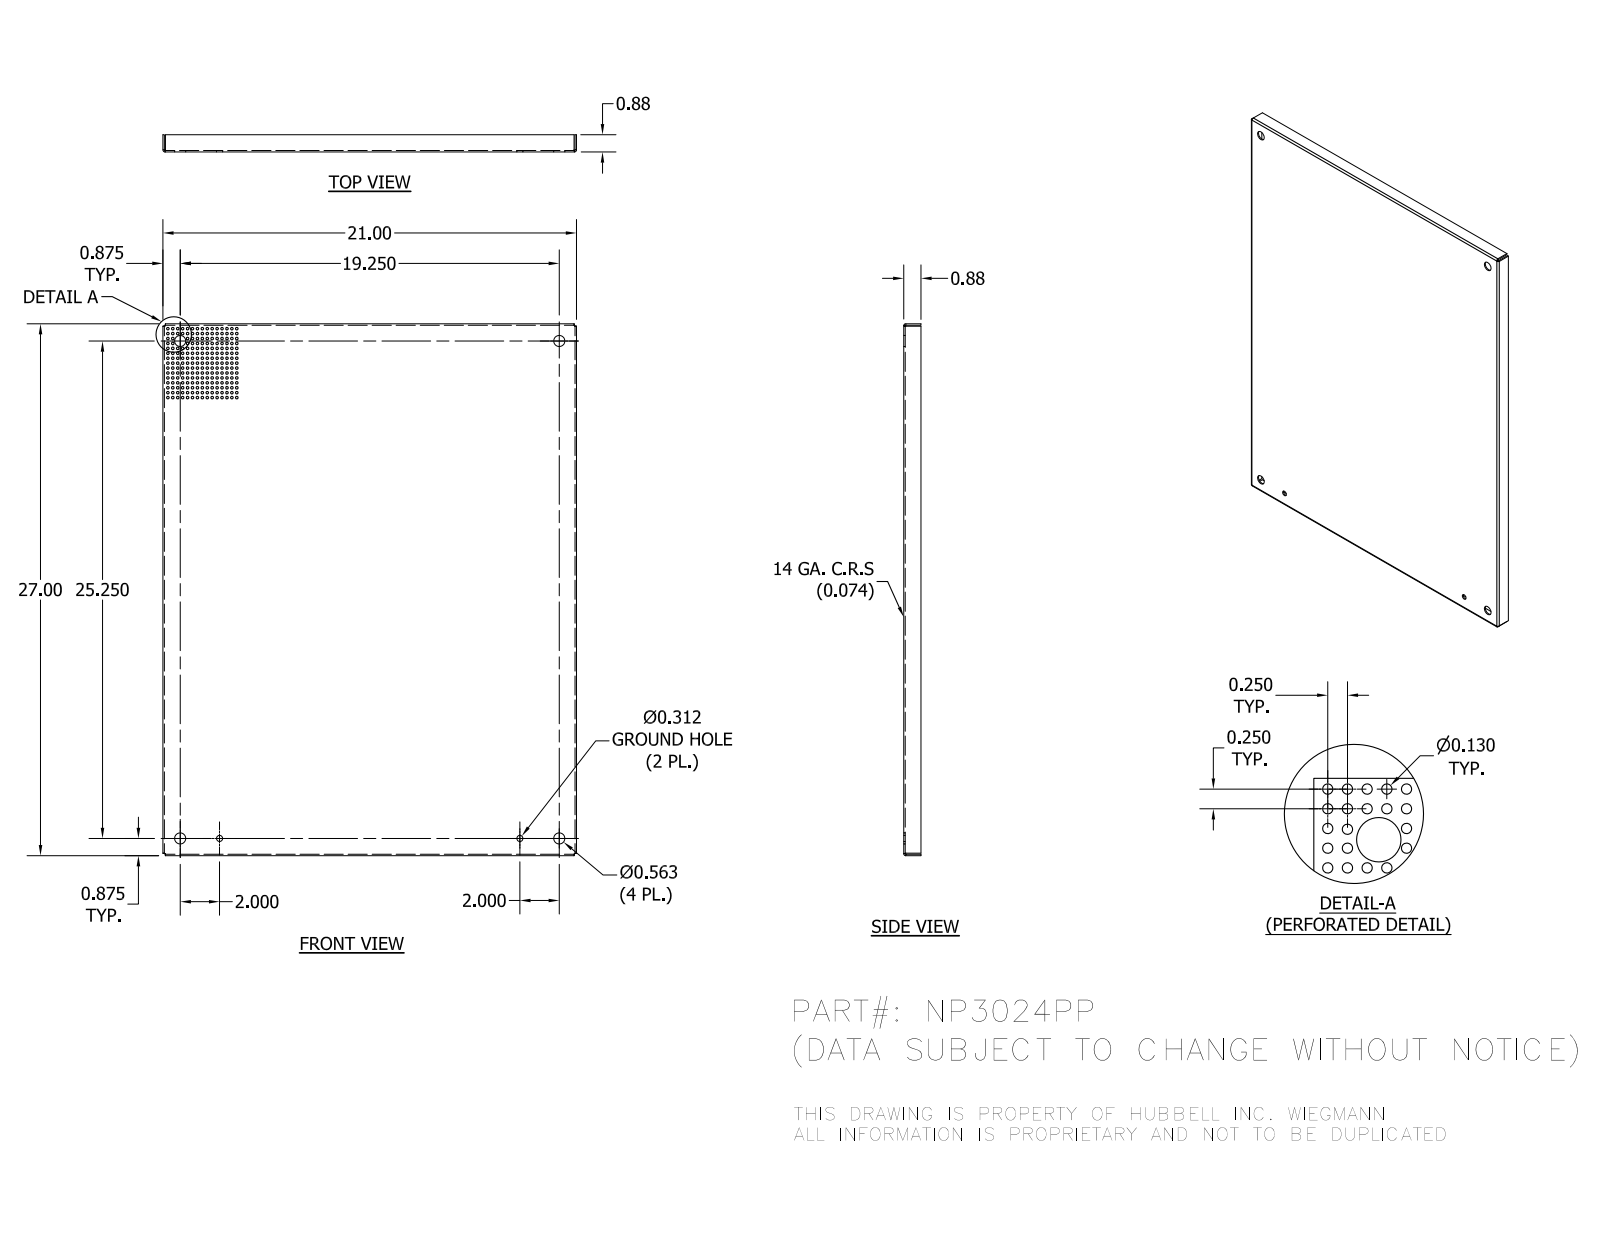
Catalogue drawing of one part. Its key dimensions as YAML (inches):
part_name: "NP3024PP"
step_written_by: "Autodesk Inventor 2012 (AUTOMOTIVE_DESIGN)"
units: inches
bodies: {solids: 1, faces: 44, planar: 22, cylindrical: 14, other: 8}
overall_size: [27, 21, 0.875]
volume: 47.29
surface_area: 1286
round_holes:
  - {diameter: 0.563, count: 4}
  - {diameter: 0.312, count: 2}
partial_cylinders:
  - {radius: 0.031, count: 4}
  - {radius: 0.105, count: 4}
face_to_face_distances: [0.074, 20.926, 26.926, 21, 20.852, 26.852, 27, 0.801, 0.875, 0.126]
hole_center_spacings: [2, 17.25, 19.25, 25.25, 25.329, 30.58, 31.751, 15.25]
